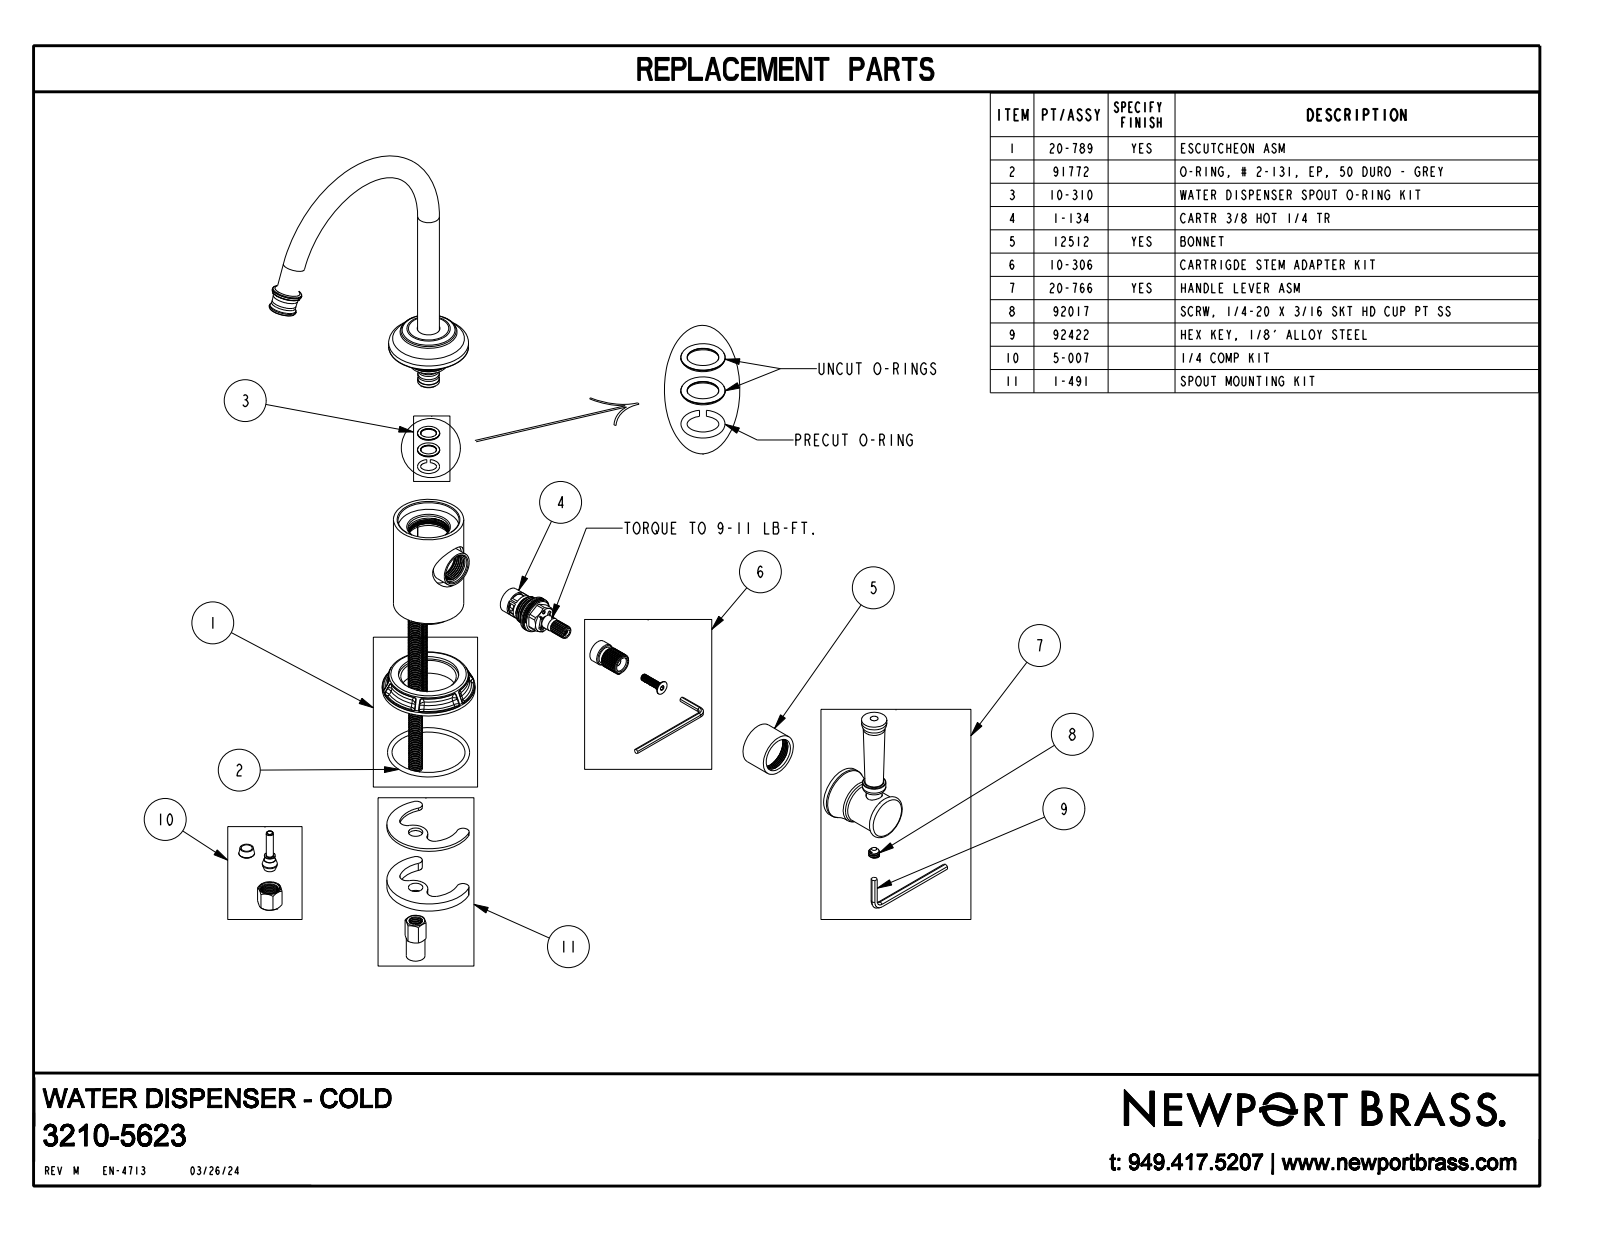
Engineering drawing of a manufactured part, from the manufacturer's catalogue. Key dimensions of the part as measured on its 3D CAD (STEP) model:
Part name (STEP PRODUCT): 3210-5623
STEP written by: CREO PARAMETRIC BY PTC INC, 2018400 (CONFIG_CONTROL_DESIGN)
Units: inches
Bodies: 1 solid, 264 faces (20 planar, 32 cylindrical, 212 other)
Overall size (bounding box): 9.373 × 6.091 × 3.708
Volume: 11.17 in³ · Surface area: 53.27 in²
Round holes (diameter × count): ⌀0.375 ×1, ⌀1 ×1
Round bosses / shafts (diameter × count): ⌀0.5 ×2, ⌀2.125 ×1, ⌀1.83 ×1, ⌀1.61 ×1, ⌀1.19 ×1, ⌀0.97 ×1, ⌀0.9 ×1, ⌀0.775 ×1
Partial cylindrical surfaces — rounded edges, fillets, slot ends (radius × count): R0.92 ×1
Main face-to-face distances: 2.723, 3.254, 0.531, 1.47, 0.425, 2.298, 2.829, 0.1, 4.364, 3.939
